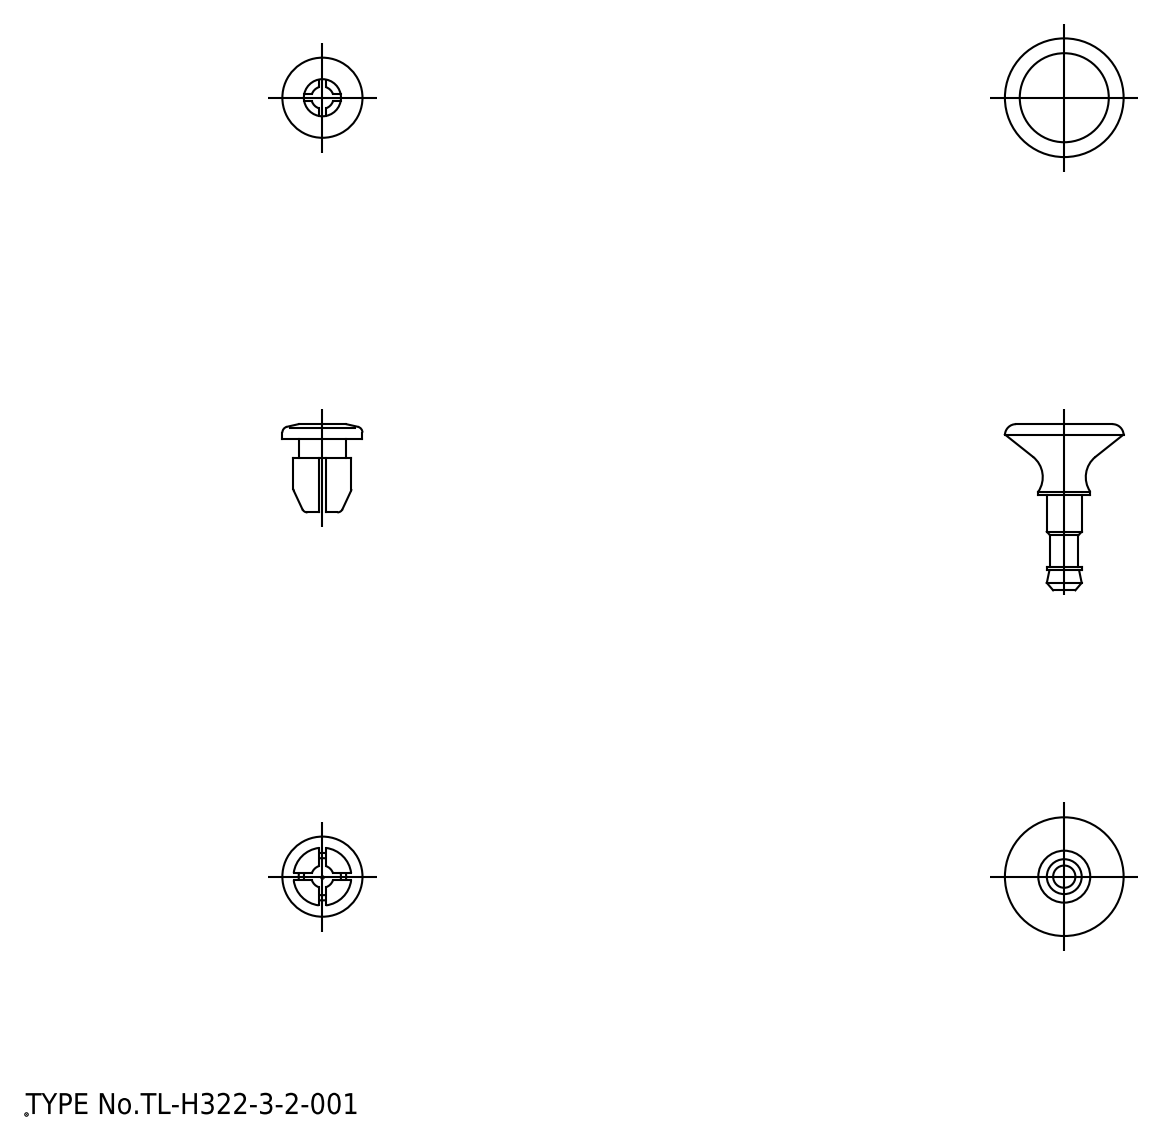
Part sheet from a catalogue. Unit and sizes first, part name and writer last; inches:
Units: inches
Overall size (bounding box): 0.961 × 0.63 × 0.63
Round holes (diameter × count): ⌀0.197 ×1
Round bosses / shafts (diameter × count): ⌀0.425 ×1, ⌀0.307 ×1, ⌀0.276 ×1, ⌀0.252 ×1, ⌀0.185 ×1, ⌀0.15 ×1
Partial cylindrical surfaces — rounded edges, fillets, slot ends (radius × count): R0.059 ×1
Main face-to-face distances: 0.039, 0.197, 0.571, 0.374, 0.079, 0.098, 0.295, 0.669, 0.177, 0.118
Volume: 0.071 in³ · Surface area: 2.165 in²
Bodies: 2 solids, 83 faces (27 planar, 22 cylindrical, 34 other)
Part name (STEP PRODUCT): grommet; plunger
STEP written by: spGate 18.9.1 (****-****-****-****) (AUTOMOTIVE_DESIGN)
